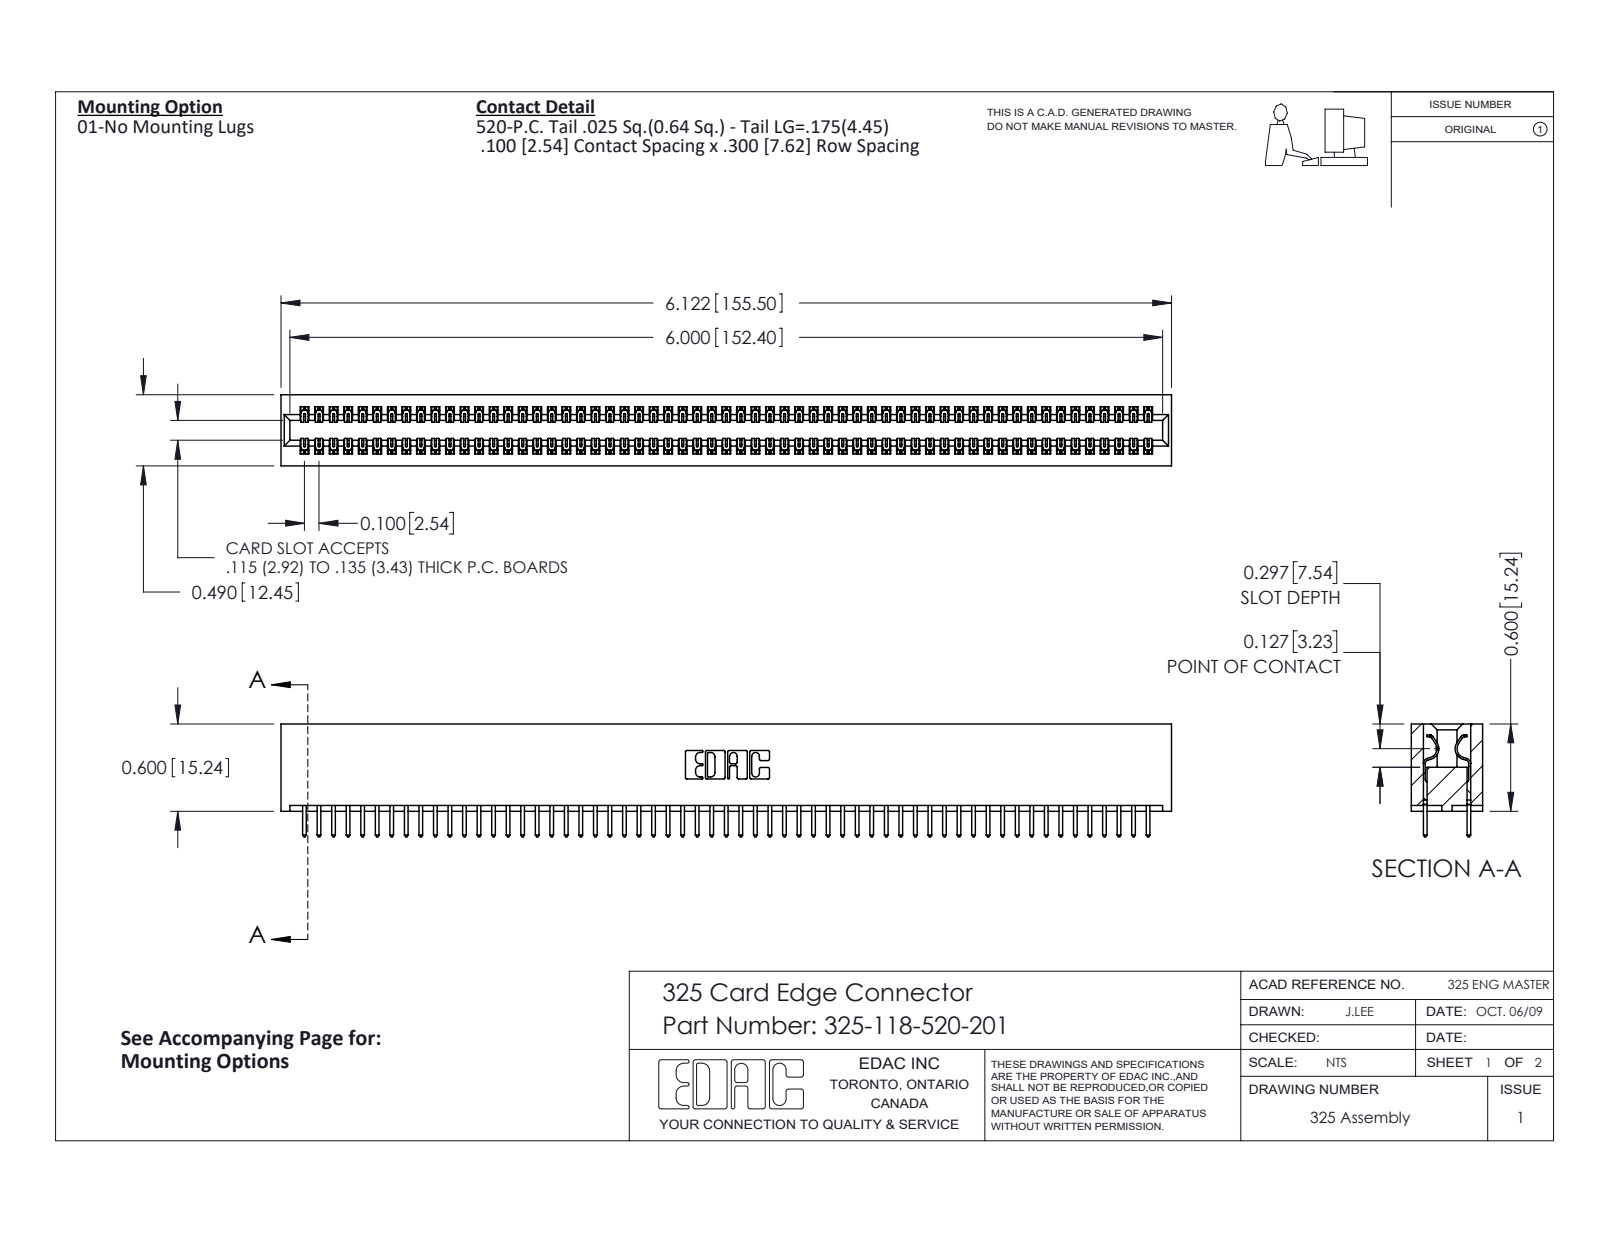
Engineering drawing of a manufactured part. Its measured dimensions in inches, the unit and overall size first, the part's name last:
Units: inches
Overall size (bounding box): 6.122 × 0.775 × 0.49
Partial cylindrical surfaces — rounded edges, fillets, slot ends (radius × count): R0.006 ×177, R0.01 ×118, R0.01 ×22, R0.007 ×6, R0.031 ×6, R0.026 ×3, R0.014 ×2, R0.022 ×2
Main face-to-face distances: 0.083, 0.407, 0.3, 0.49, 0.107, 0.383, 0.025, 0.325, 0.275, 0.56
Volume: 1.27 in³ · Surface area: 40.33 in²
Bodies: 119 solids, 6242 faces (4314 planar, 1928 cylindrical, 0 other)
Part name (STEP PRODUCT): 325-292-001_325-293-120; 325 Part_Lugless; 325-118-520-201
STEP written by: SolidWorks 2016 (CONFIG_CONTROL_DESIGN)
